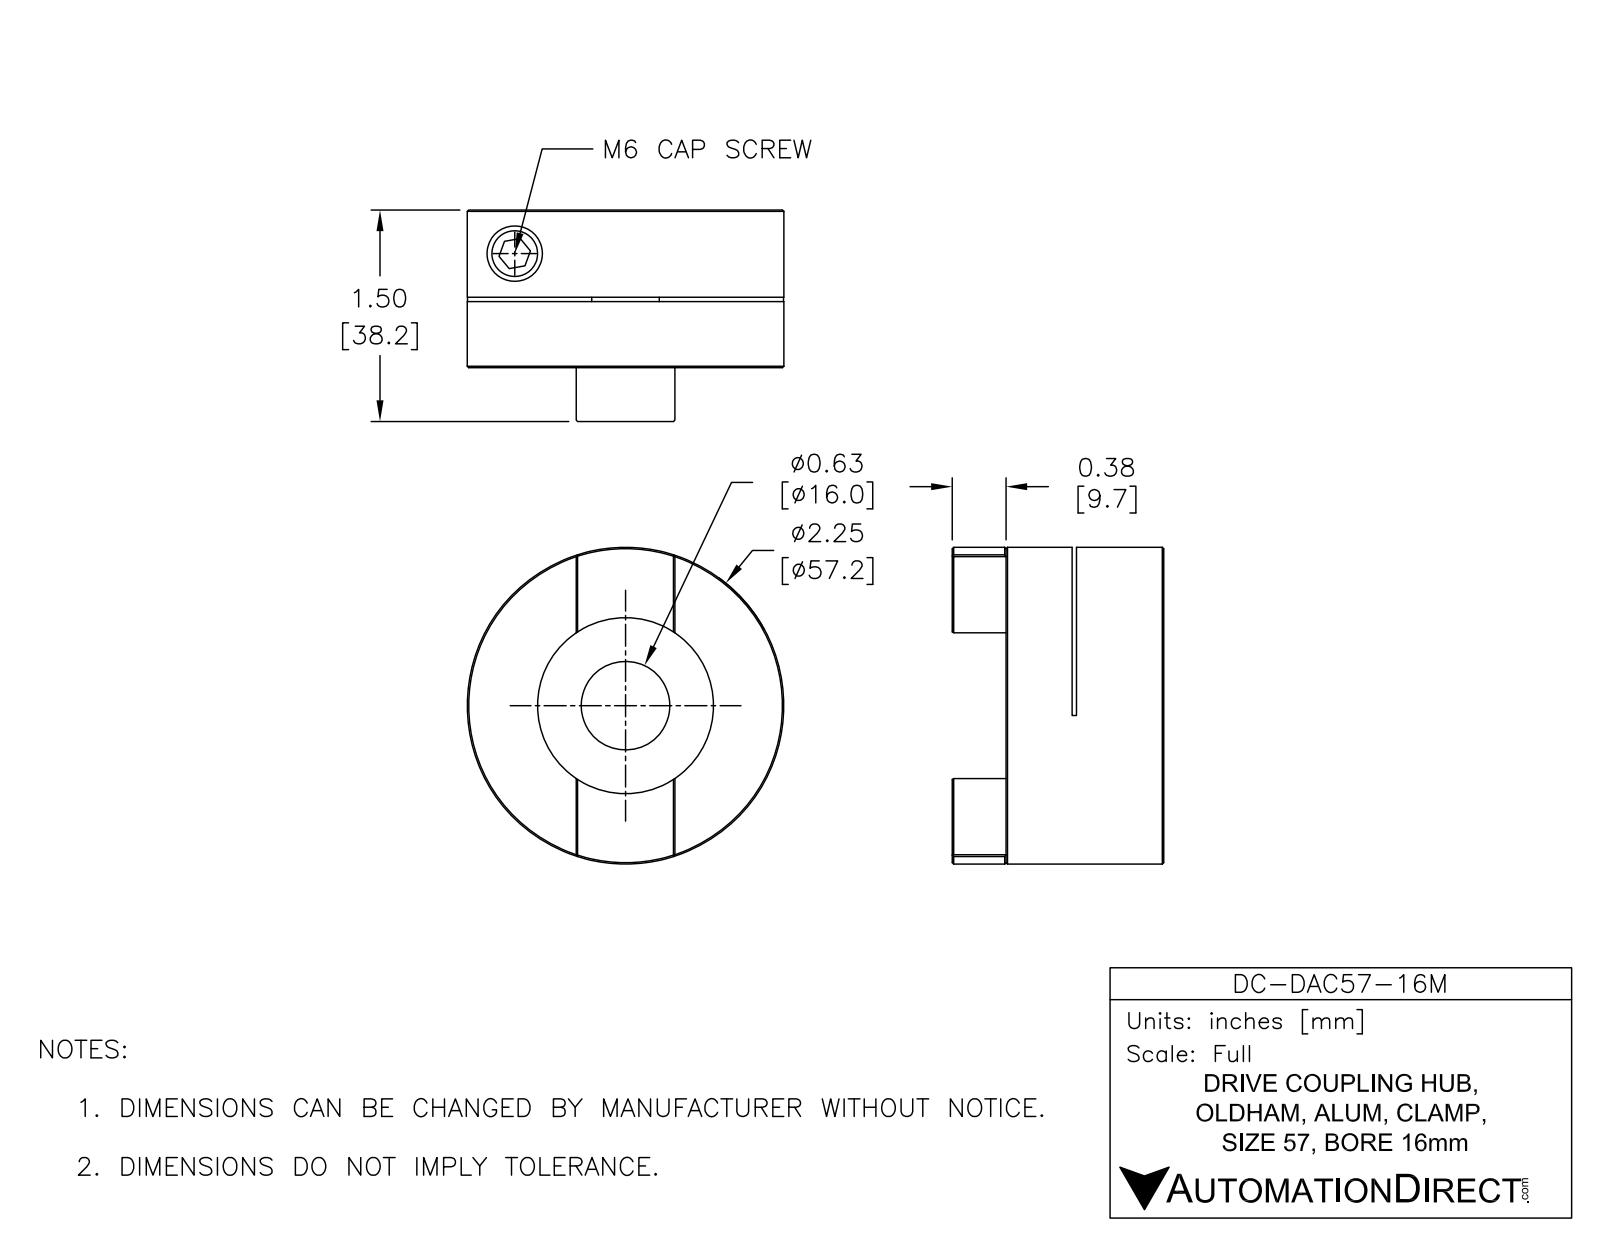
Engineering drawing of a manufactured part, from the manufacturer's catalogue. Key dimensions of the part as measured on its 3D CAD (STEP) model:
Part name (STEP PRODUCT): DC-DAC57-16M
STEP written by: SolidWorks 2015 (AUTOMOTIVE_DESIGN)
Units: millimetres
Bodies: 1 solid, 55 faces (29 planar, 16 cylindrical, 10 other)
Overall size (bounding box): 57.15 × 57.15 × 38.16
Volume: 70 201 mm³ · Surface area: 16 326 mm²
Round holes (diameter × count): ⌀4.93 ×1, ⌀6.6 ×1, ⌀11 ×1, ⌀12.7 ×1, ⌀31.75 ×1
Round bosses / shafts (diameter × count): ⌀57.15 ×1
Main face-to-face distances: 16.54, 28.45, 11.91, 15.75, 0.79, 12.7, 28, 12.25, 11.46, 0.45
